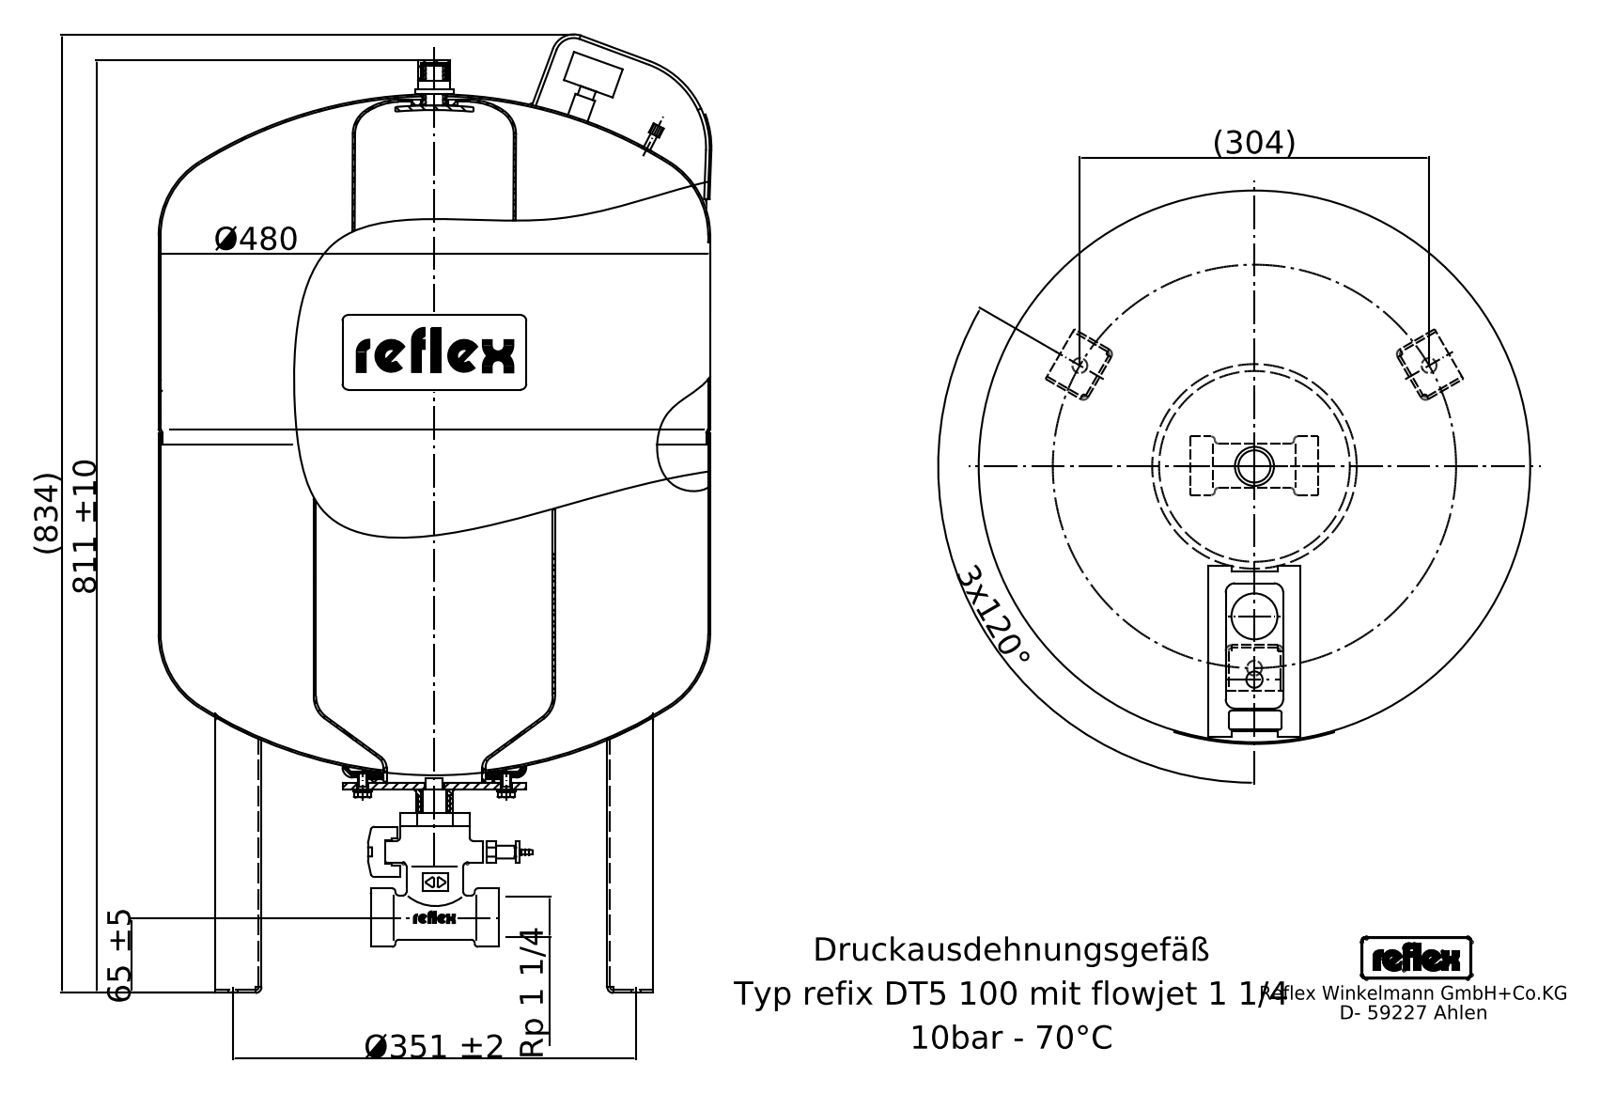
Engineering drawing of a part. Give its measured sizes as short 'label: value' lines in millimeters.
written by: Mechanical Desktop 2008 (CONFIG_CONTROL_DESIGN)
unit: mm
bodies: 21 solids, 683 faces (289 planar, 251 cylindrical, 143 other)
size: 828.24 × 480 × 480
volume: 91 370 000 mm³; area: 2 145 000 mm²
holes: 3× ⌀13.4, 1× ⌀2.48, 1× ⌀3.8, 1× ⌀4.3, 1× ⌀4.4, 1× ⌀5.45, 1× ⌀7, 1× ⌀8, 1× ⌀11.4, 1× ⌀42.4, 1× ⌀92, 1× ⌀150
bosses: 9× ⌀10, 2× ⌀18, 2× ⌀13, 1× ⌀480, 1× ⌀160, 1× ⌀140, 1× ⌀62, 1× ⌀56
rounds: 20× R0.5, 15× R1, 15× R2.5, 15× R5, 4× R3.94, 3× R1.57, 2× R2.69, 2× R4.72
face distances: 323, 2.5, 47.5, 50, 45, 141, 464, 6, 147, 470
hole spacings: 175.5, 303.98
